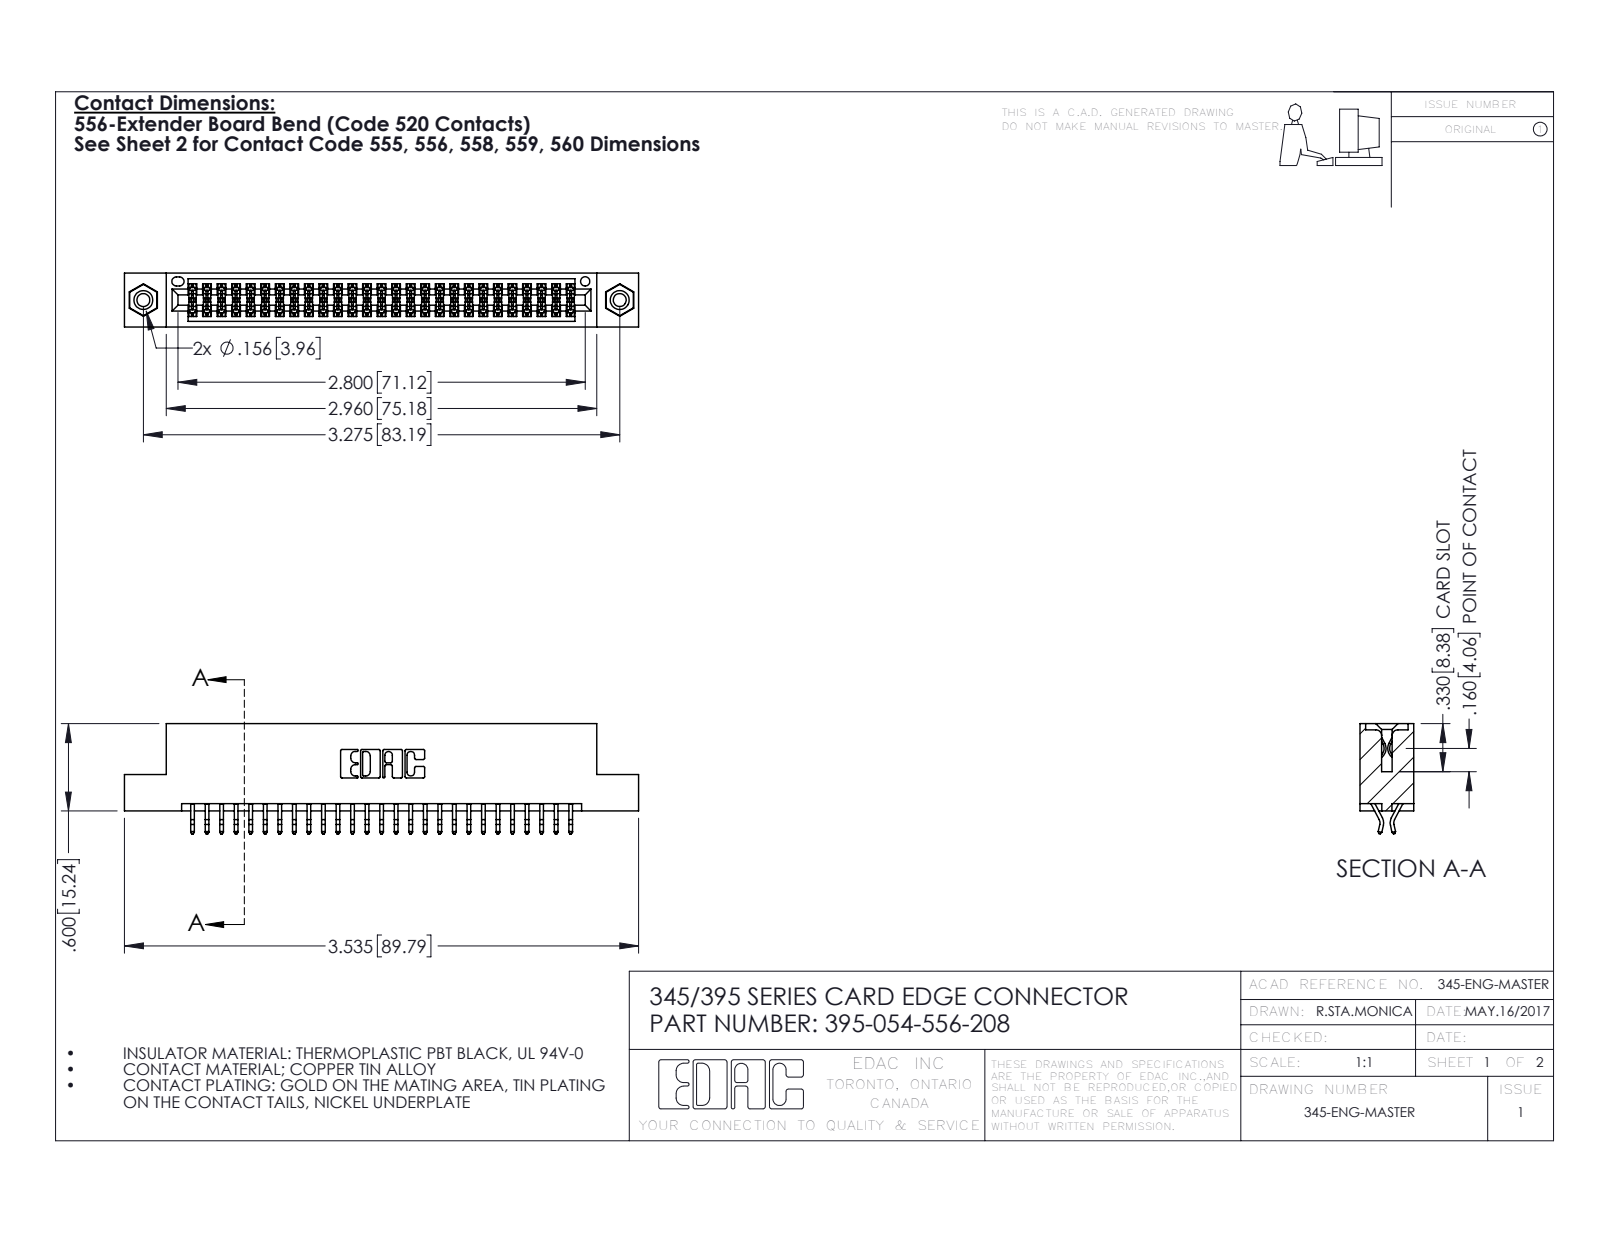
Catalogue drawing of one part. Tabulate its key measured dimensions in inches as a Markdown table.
| quantity | value |
| --- | --- |
| part name | 345-292-001_556 Tail; 395-054-556-208; 345-250-001_345-250-003-102; 345 Part_Flush Mounting Lugs - 0.156 Dia-TI |
| STEP written by | SolidWorks 2016 (CONFIG_CONTROL_DESIGN) |
| units | inches |
| bodies | 57 solids, 3210 faces (2110 planar, 1084 cylindrical, 16 other) |
| overall size | 3.535 × 0.757 × 0.37 |
| volume | 0.523 in³ |
| surface area | 19.14 in² |
| round holes (diameter × count) | 0.089 × 2, 0.125 × 2, 0.156 × 2, 0.064 × 1 |
| round bosses / shafts (diameter × count) | 0.155 × 2 |
| partial cylindrical surfaces (radius × count) | 0.006 × 81, 0.01 × 22, 0.007 × 6, 0.031 × 6, 0.026 × 3, 0.01 × 2, 0.014 × 2, 0.019 × 2 |
| main face-to-face distances | 0.072, 0.298, 0.2, 0.37, 0.025, 0.098, 0.272, 0.225, 0.175, 0.149 |
| hole center spacings | 0.27, 3.04, 3.275 |
